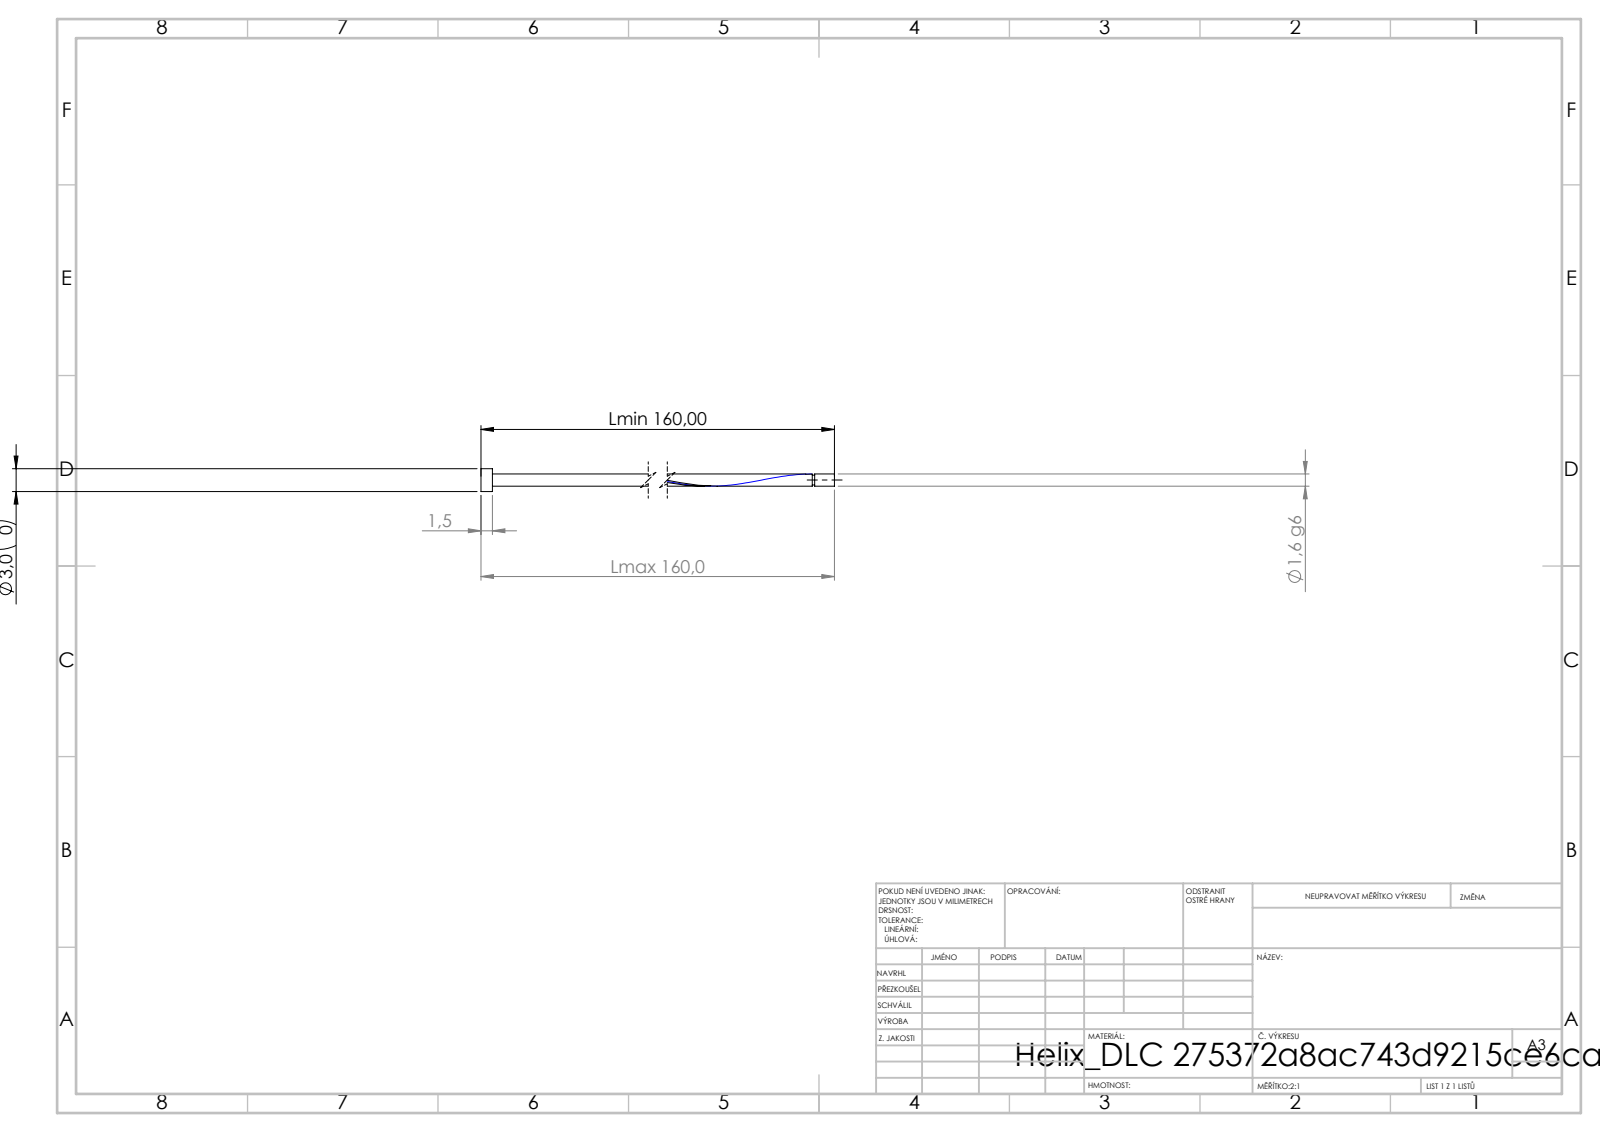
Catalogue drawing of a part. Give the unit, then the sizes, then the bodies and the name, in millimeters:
Units: millimetres
Overall size (bounding box): 160 × 3 × 3
Round bosses / shafts (diameter × count): ⌀3 ×1, ⌀1.6 ×1, ⌀1.28 ×1
Main face-to-face distances: 1.5, 160, 158.5, 157.41, 155.91, 2.59, 157.09, 155.59, 0.32, 2.91
Volume: 397 mm³ · Surface area: 1 106 mm²
Bodies: 1 solid, 16 faces (6 planar, 9 cylindrical, 1 other)
STEP written by: SolidWorks 2019 (CONFIG_CONTROL_DESIGN)
